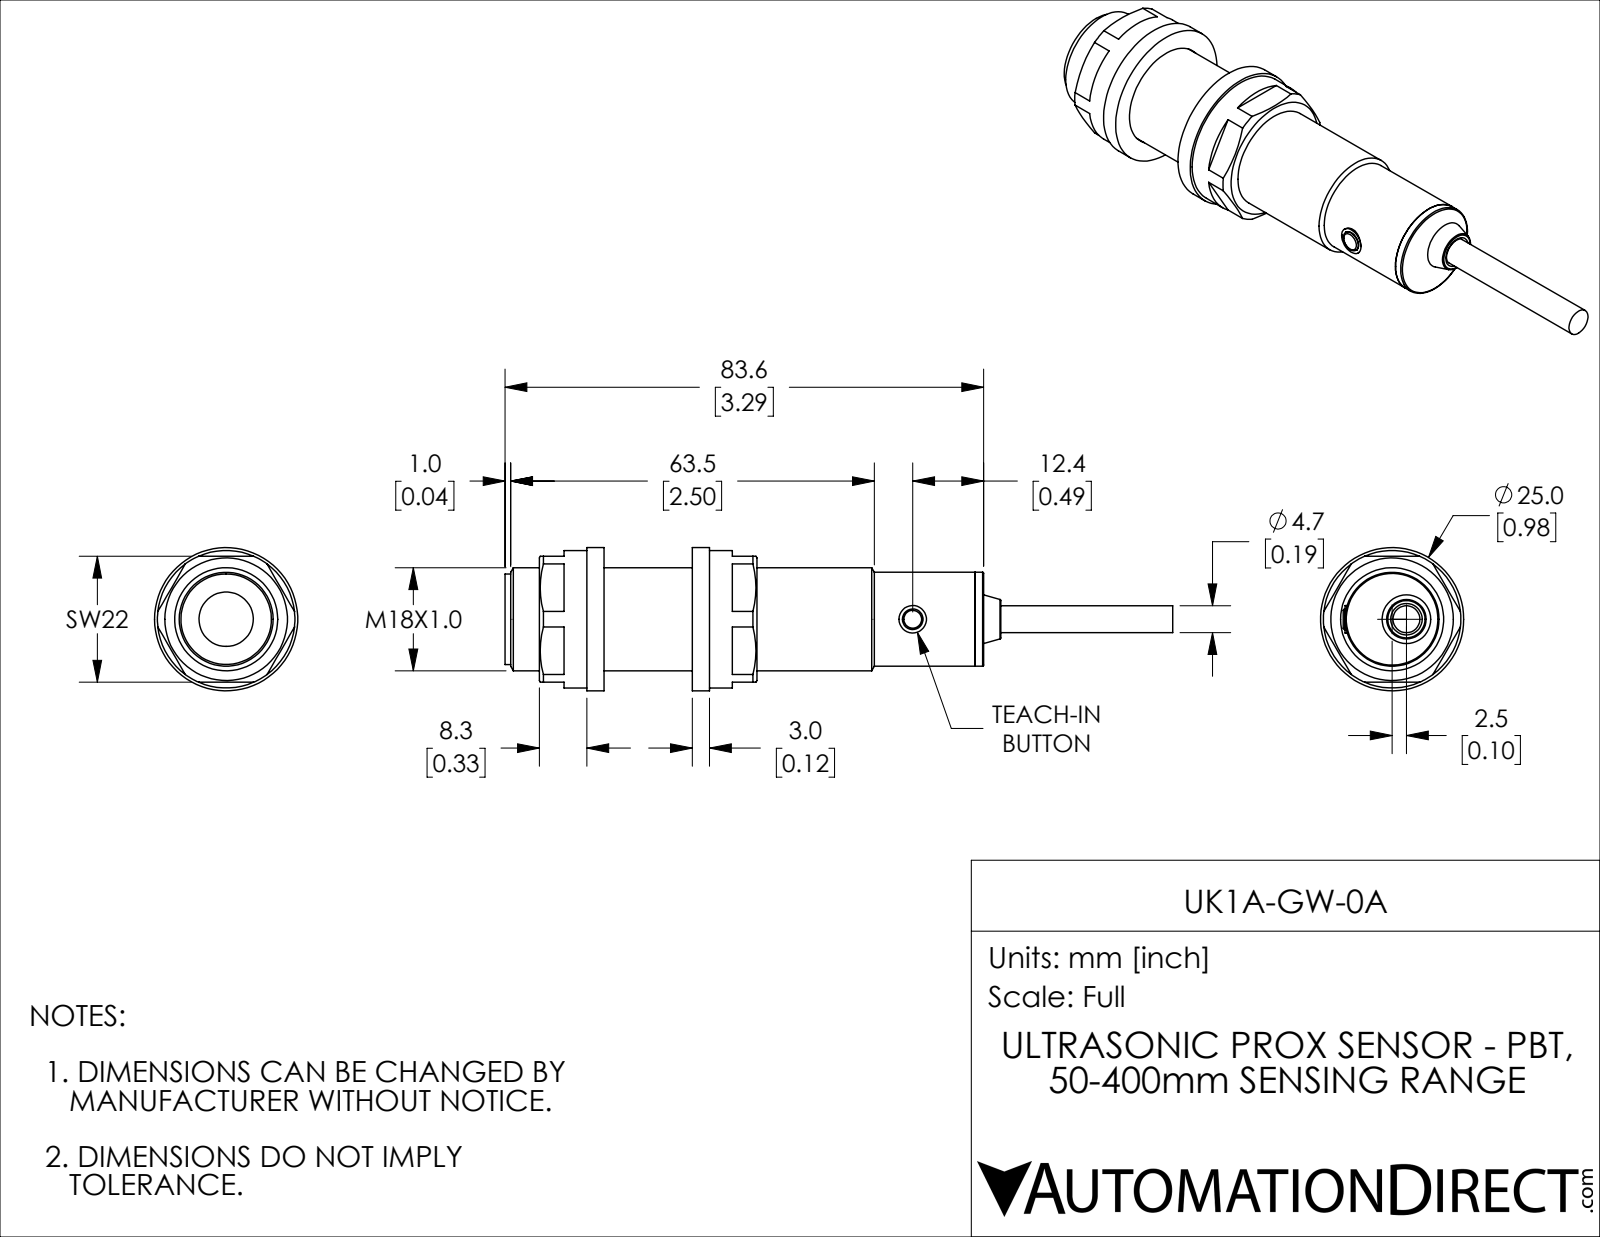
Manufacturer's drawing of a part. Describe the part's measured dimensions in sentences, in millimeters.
The part is named "UK1A-GW-0A". Its 3-D file was written by "SolidWorks 2018 (AUTOMOTIVE_DESIGN)". It is 10 solids with 107 faces: 49 planar, 40 cylindrical and 18 other. Overall it measures 116.6 by 25 by 25 millimeters. Its volume is 25 220 cubic millimeters and its surface area 11 419 square millimeters. Round holes: 2 of diameter 4.7, 1 of diameter 3.6, 1 of diameter 9.5, 1 of diameter 18, 1 of diameter 18.2. Round bosses or shafts: 1 of diameter 25, 1 of diameter 24, 1 of diameter 16.4, 1 of diameter 15.8, 1 of diameter 5.4, 1 of diameter 4.8. The main face-to-face distances are 3, 18.4, 21.4, 67.8, 46.4, 13.3, 34.7, 81.1, 16.3, 64.8. The hole center spacings are 2.5.
